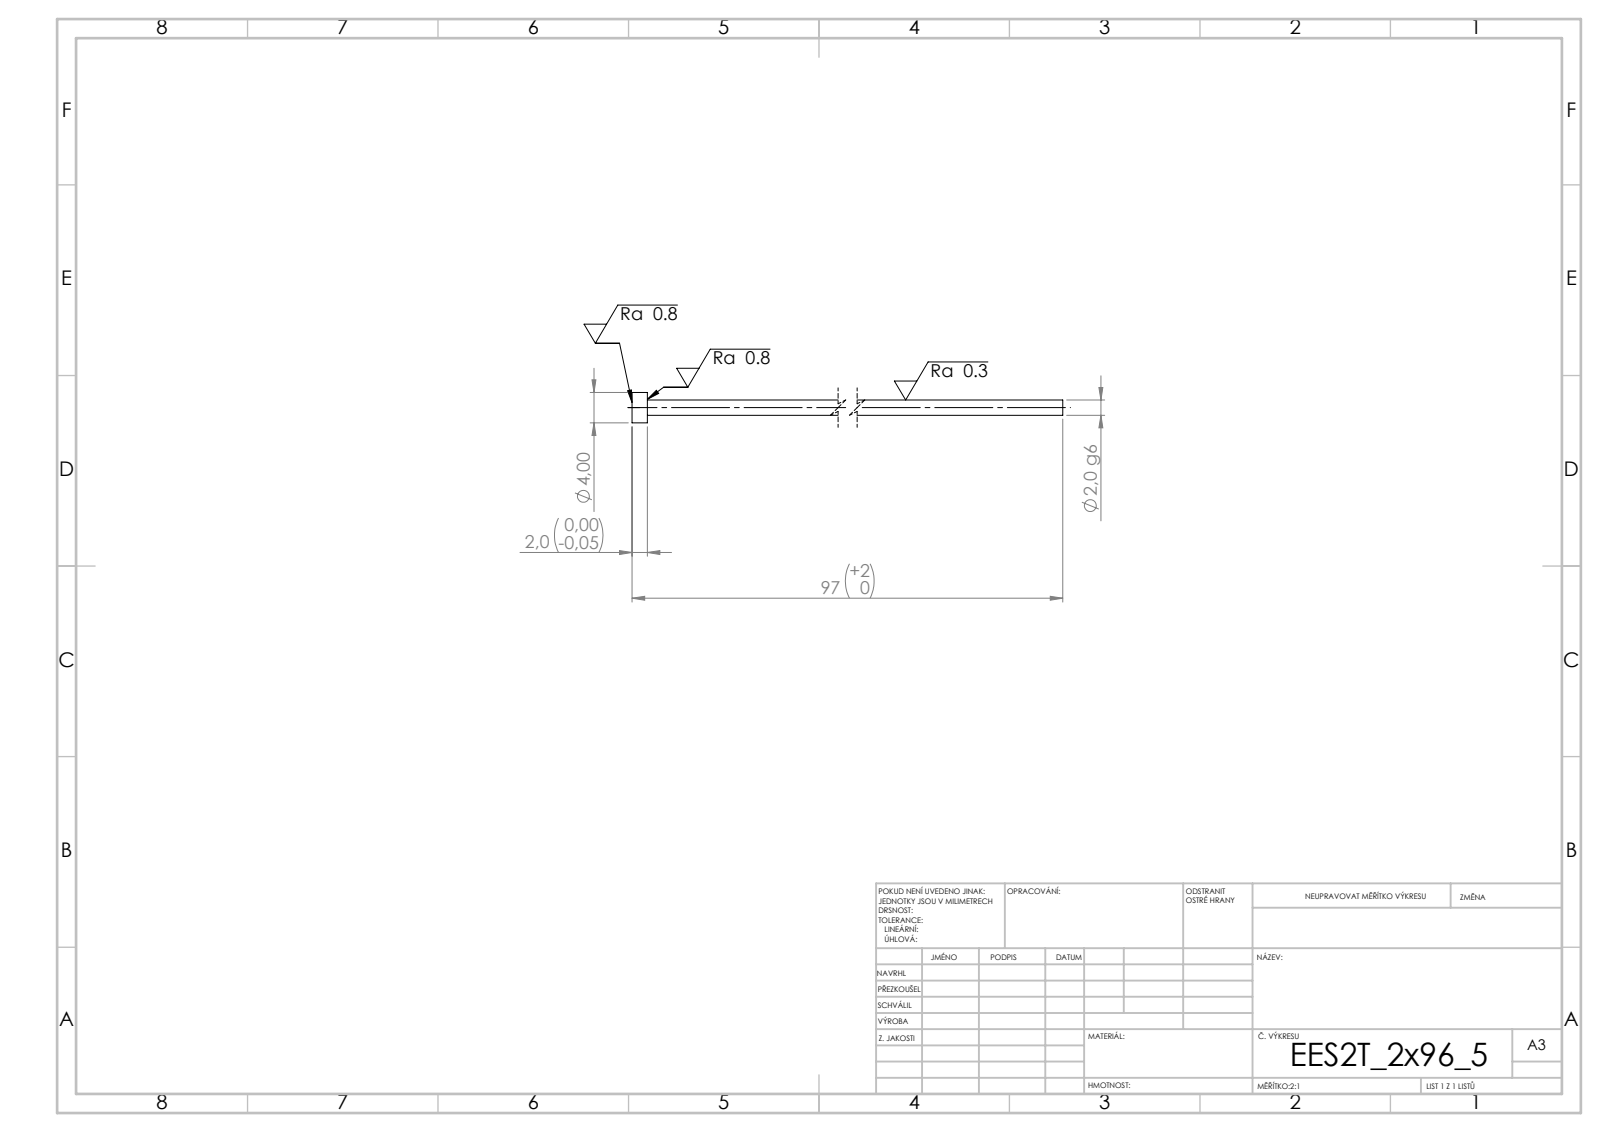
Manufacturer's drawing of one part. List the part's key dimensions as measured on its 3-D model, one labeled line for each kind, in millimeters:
STEP written by: SolidWorks 2019 (CONFIG_CONTROL_DESIGN)
Units: millimetres
Bodies: 1 solid, 7 faces (3 planar, 4 cylindrical, 0 other)
Overall size (bounding box): 96.5 × 4 × 4
Volume: 322 mm³ · Surface area: 644 mm²
Round bosses / shafts (diameter × count): ⌀4 ×1, ⌀2 ×1
Main face-to-face distances: 2, 96.5, 94.5
